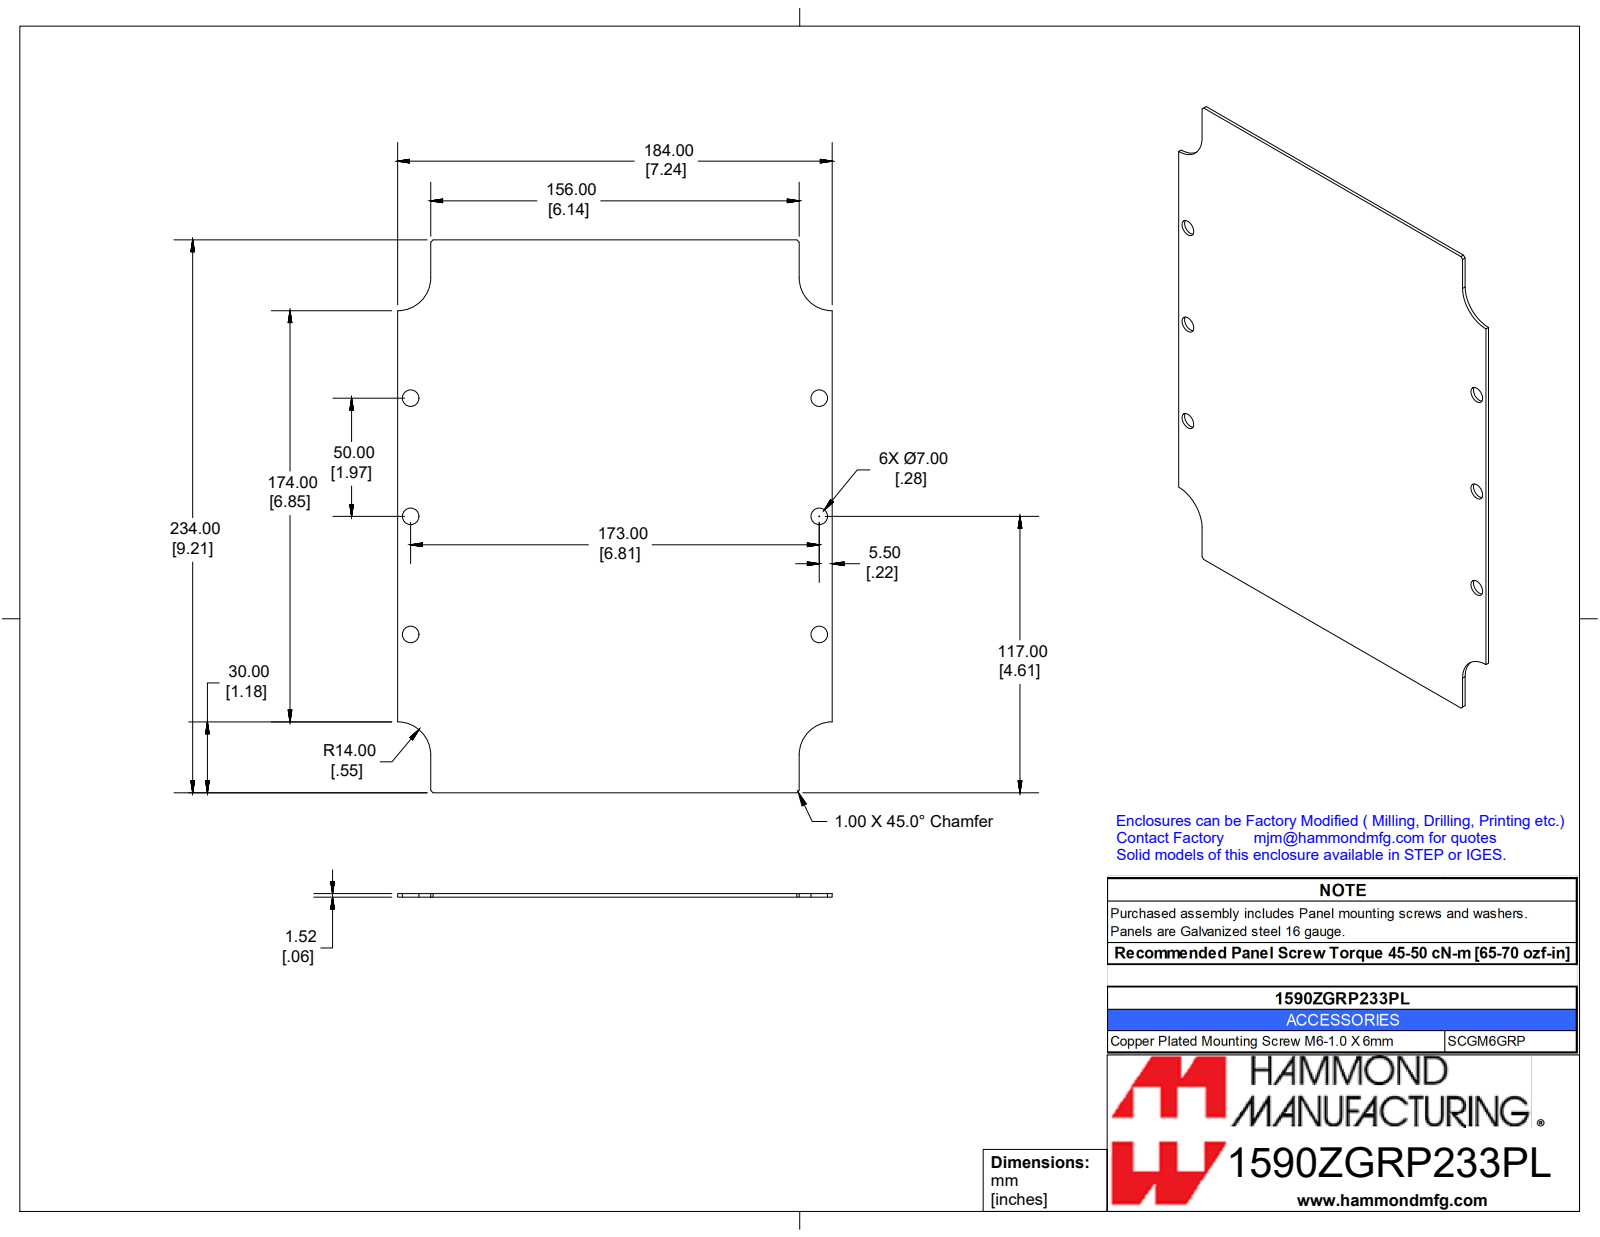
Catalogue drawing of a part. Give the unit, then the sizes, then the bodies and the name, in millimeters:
Units: millimetres
Overall size (bounding box): 234 × 184 × 1.5
Round holes (diameter × count): ⌀7 ×6
Partial cylindrical surfaces — rounded edges, fillets, slot ends (radius × count): R14 ×4
Main face-to-face distances: 1.5, 184, 234, 14, 170, 156, 274.3
Hole centre spacings: 50, 180.1, 173, 100, 199.8
Volume: 62 960 mm³ · Surface area: 84 060 mm²
Bodies: 1 solid, 24 faces (14 planar, 10 cylindrical, 0 other)
Part name (STEP PRODUCT): 1590ZGRP233PL
STEP written by: SolidWorks 2019 (CONFIG_CONTROL_DESIGN)
